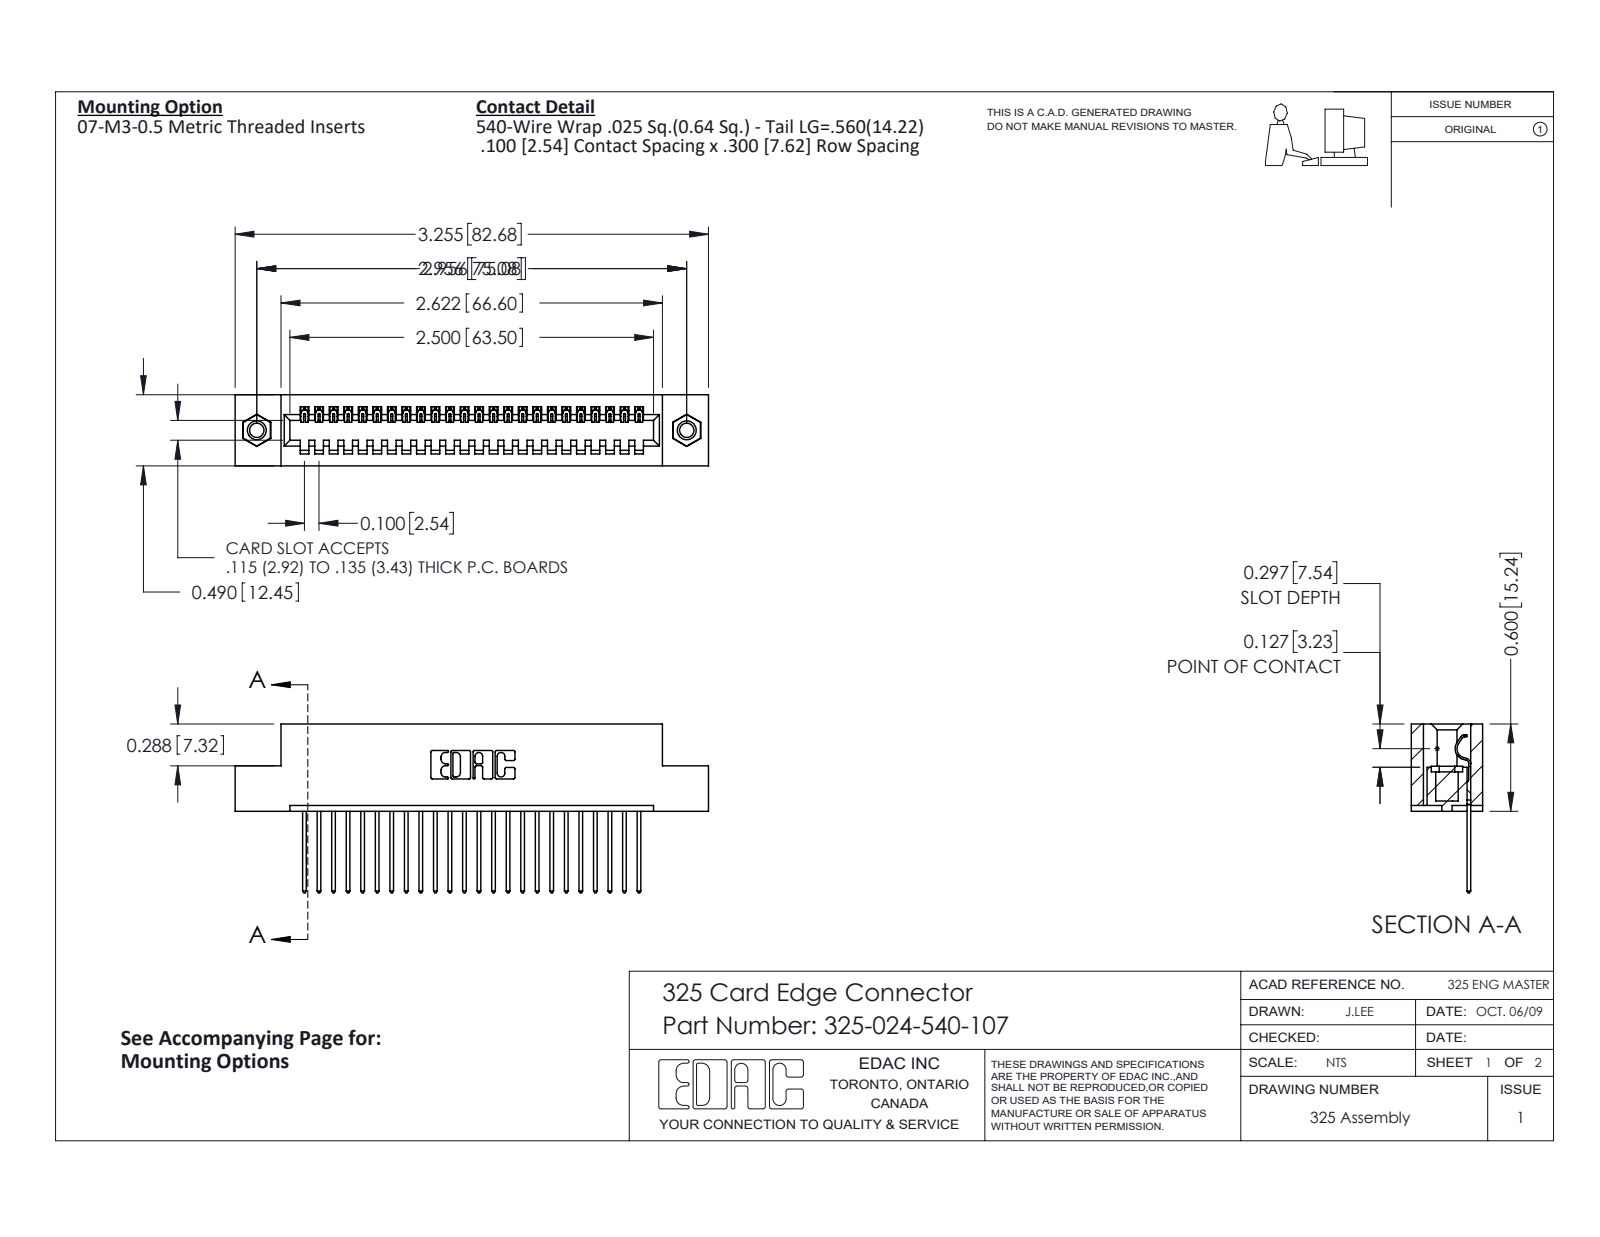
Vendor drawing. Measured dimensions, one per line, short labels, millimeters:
name: 325-292-001_325-293-140; 325-024-540-107; 325 Part_TI; 345-250-001_345-250-005-103
written by: SolidWorks 2016 (CONFIG_CONTROL_DESIGN)
unit: mm
bodies: 27 solids, 1566 faces (1110 planar, 440 cylindrical, 16 other)
size: 82.7 × 29.5 × 12.4
volume: 10 400 mm³; area: 11 300 mm²
holes: 2× ⌀2.5, 2× ⌀3.2, 2× ⌀4.1
bosses: 2× ⌀3.9
rounds: 48× R0.2, 48× R0.3, 22× R0.3, 6× R0.2, 6× R0.8, 3× R0.7, 1× R0.4, 1× R0.6
face distances: 2.1, 10.3, 7.6, 12.4, 2.7, 9.7, 0.6, 1, 8.3, 15.2
hole spacings: 75.1
